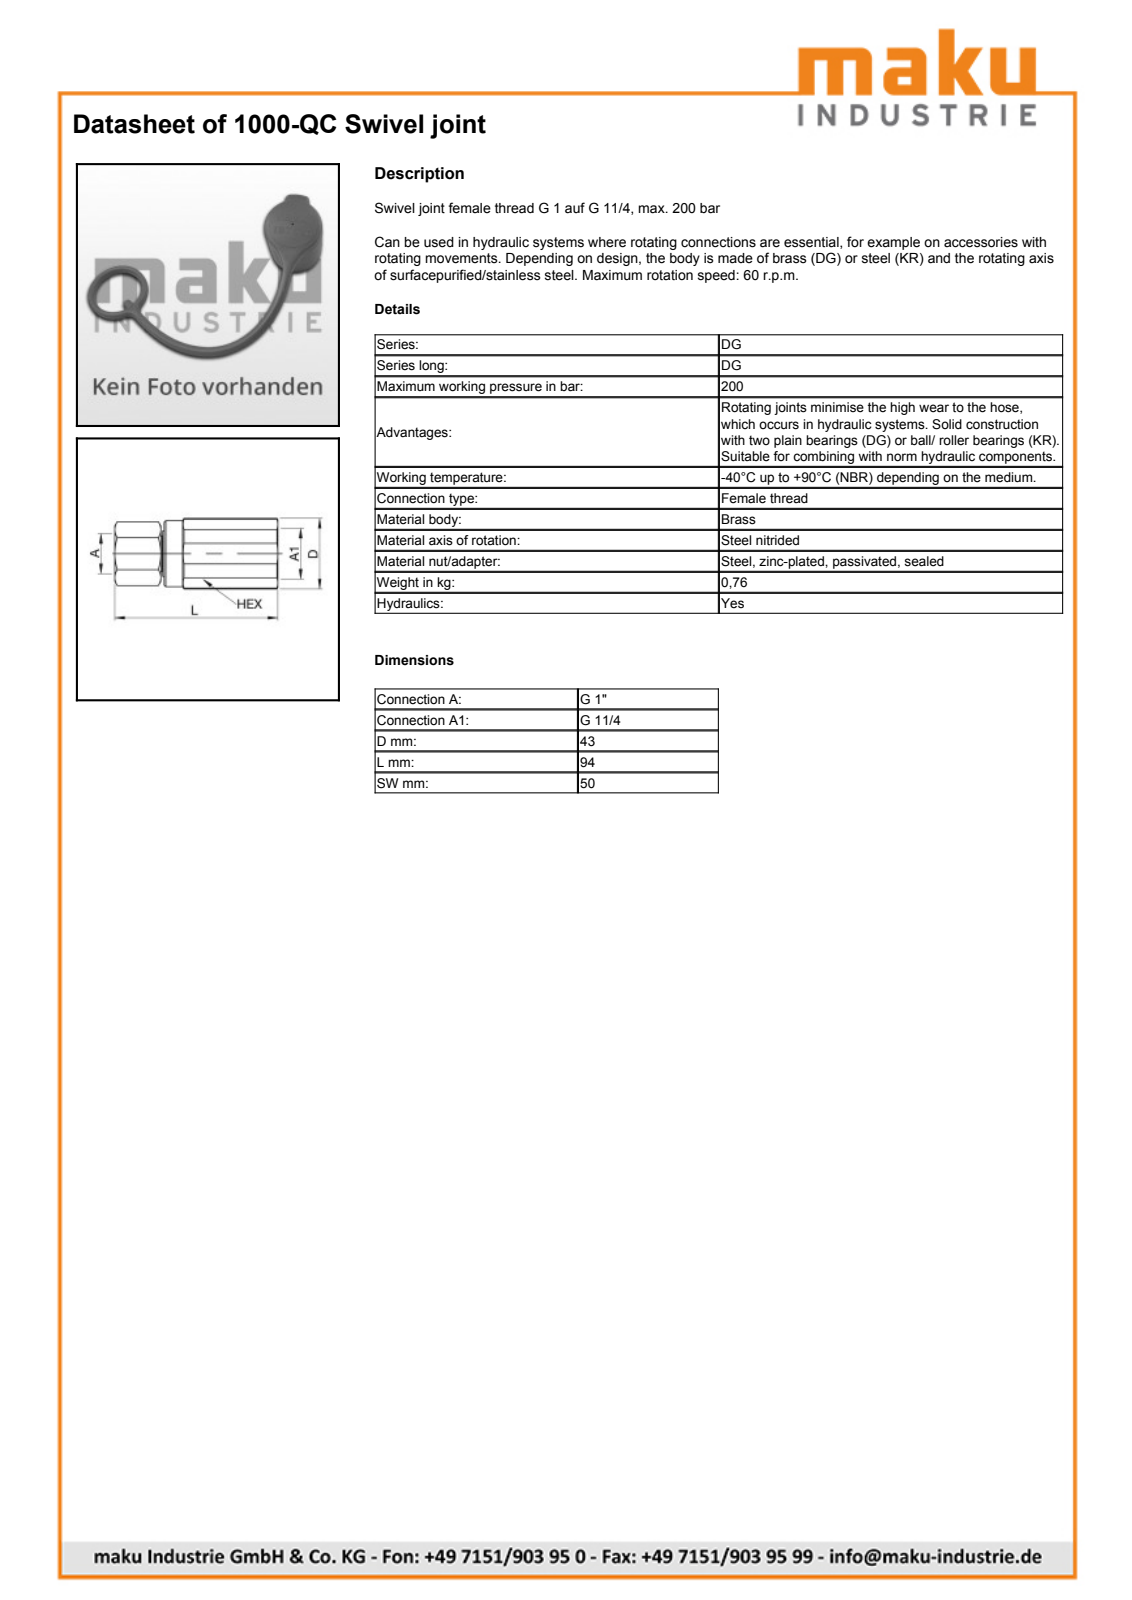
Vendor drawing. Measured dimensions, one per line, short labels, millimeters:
name: 1000-QC
written by: SolidWorks 2009 (AUTOMOTIVE_DESIGN)
unit: mm
bodies: 1 solid, 106 faces (29 planar, 29 cylindrical, 48 other)
size: 93.85 × 53 × 50
volume: 104 766 mm³; area: 28 196 mm²
holes: 1× ⌀3.2, 1× ⌀22, 1× ⌀30.5, 1× ⌀30.6, 1× ⌀39
bosses: 1× ⌀49, 1× ⌀37.8, 1× ⌀30
rounds: 1× R17.88, 1× R20, 1× R26.5
face distances: 6, 44, 50, 38, 37, 61, 24, 7.35, 44.35, 68.35
